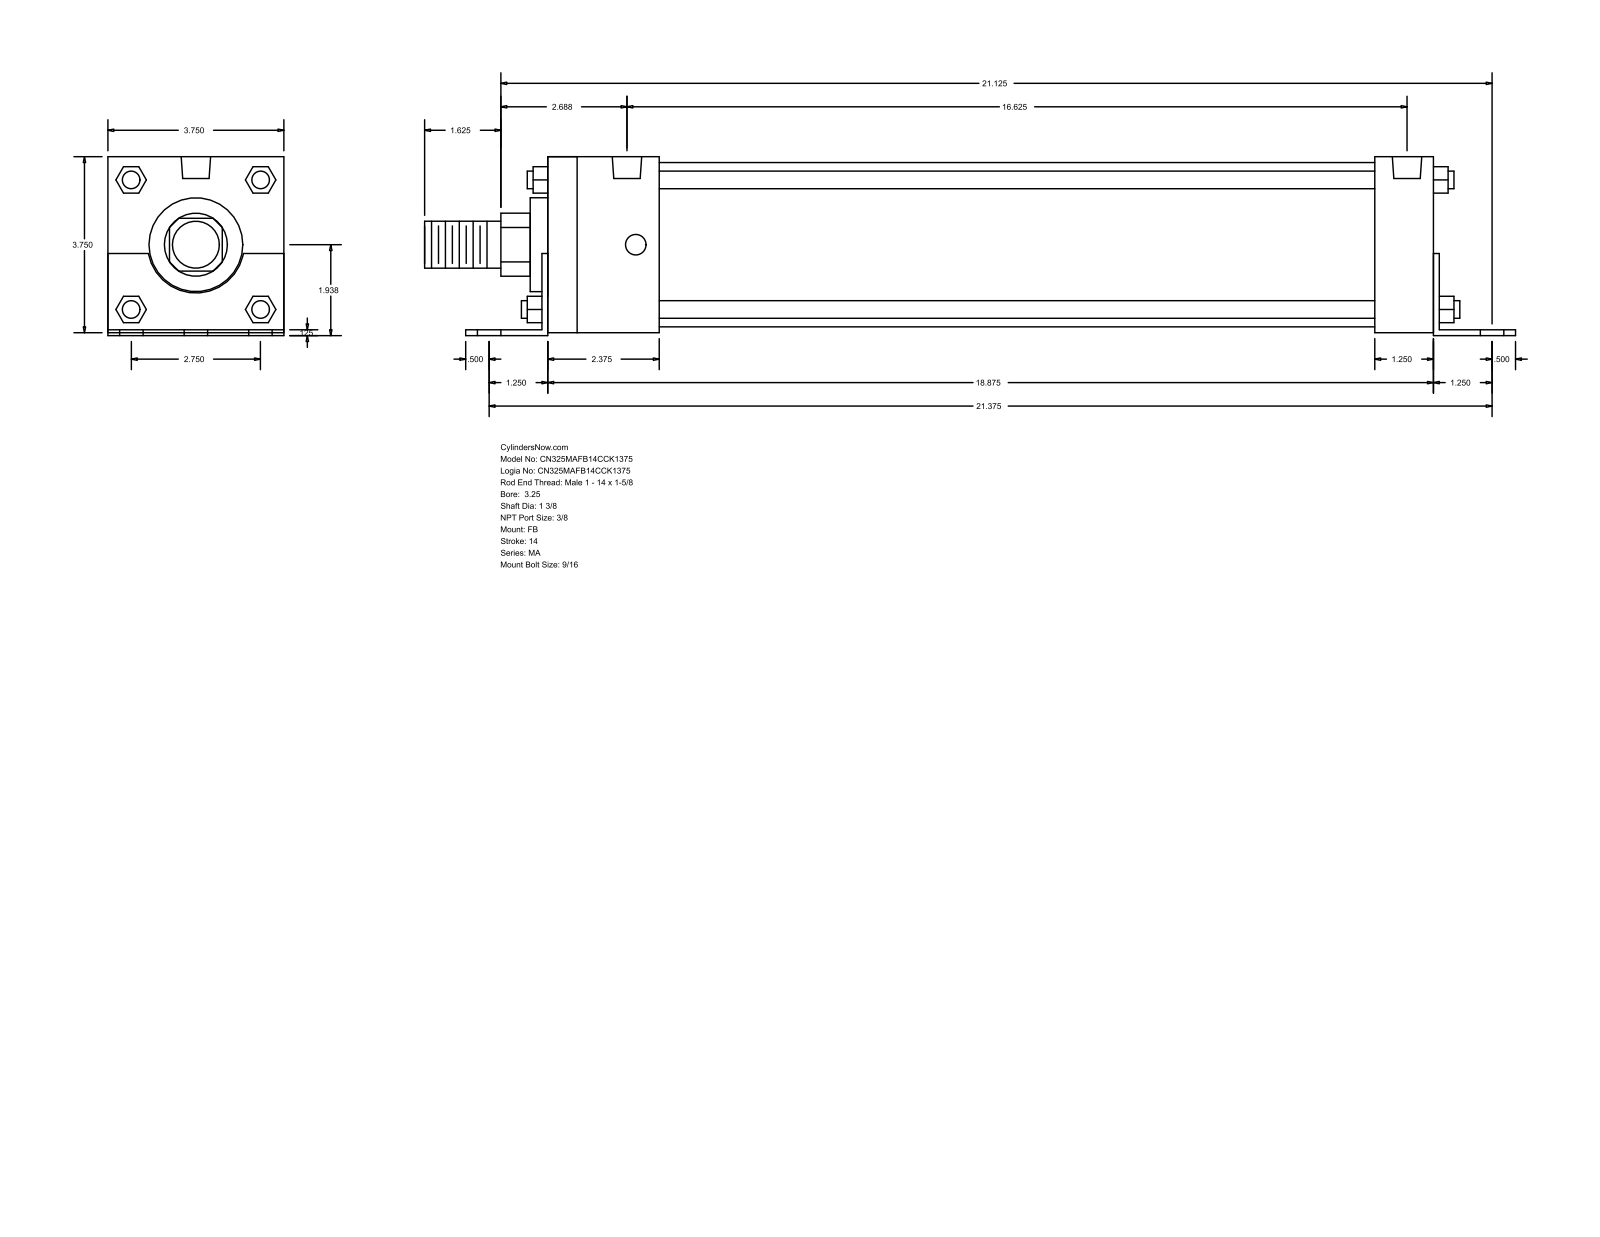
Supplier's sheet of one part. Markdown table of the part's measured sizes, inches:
| quantity | value |
| --- | --- |
| part name | MA_FB__0325_1.375 |
| STEP written by | GSSL Pune (CONFIG_CONTROL_DESIGN) |
| units | inches |
| bodies | 0 solids, 140 faces (105 planar, 35 cylindrical, 0 other) |
| overall size | 23.25 × 3.813 × 3.75 |
| round holes (diameter × count) | 0.563 × 6, 0.437 × 4, 0.627 × 2 |
| round bosses / shafts (diameter × count) | 0.375 × 4, 3.5 × 1, 2 × 1, 1.375 × 1, 1 × 1 |
| partial cylindrical surfaces (radius × count) | 0.672 × 1, 1.03 × 1 |
| main face-to-face distances | 3.75, 0.125, 0.063, 3.812, 0.062, 3.687, 0.125, 18.875, 19, 1.25 |
| hole center spacings | 1.375, 21.419, 21.375, 0.188, 2.275, 2.427, 2.75, 3.243 |
